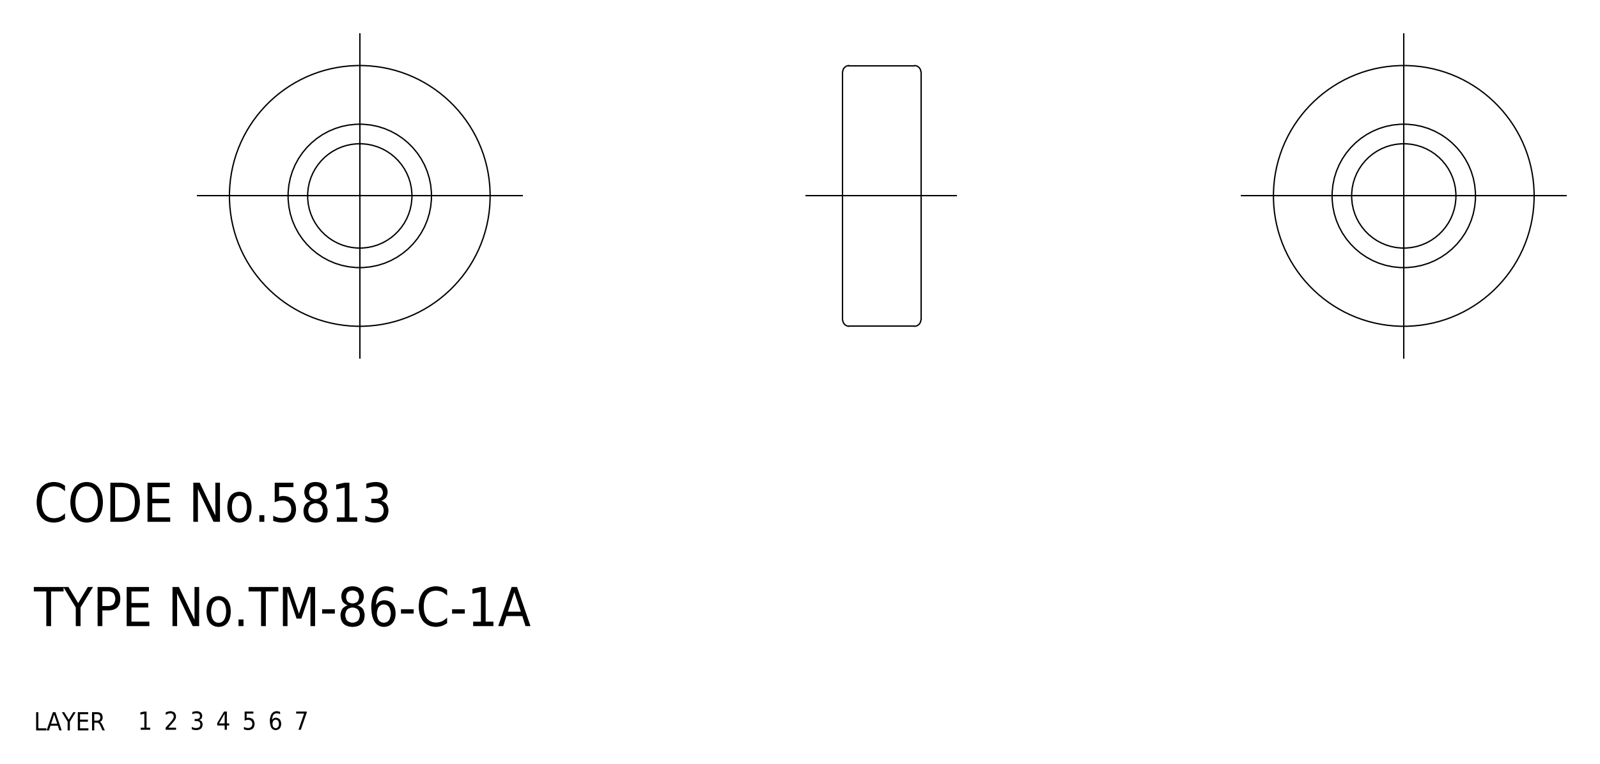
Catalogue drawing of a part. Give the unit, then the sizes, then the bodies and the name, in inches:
Units: inches
Overall size (bounding box): 0.787 × 0.787 × 0.236
Volume: 0.096 in³ · Surface area: 2.353 in²
Bodies: 1 solid, 28 faces (0 planar, 0 cylindrical, 28 other)
Part name (STEP PRODUCT): roller
STEP written by: CADfix (AUTOMOTIVE_DESIGN)
